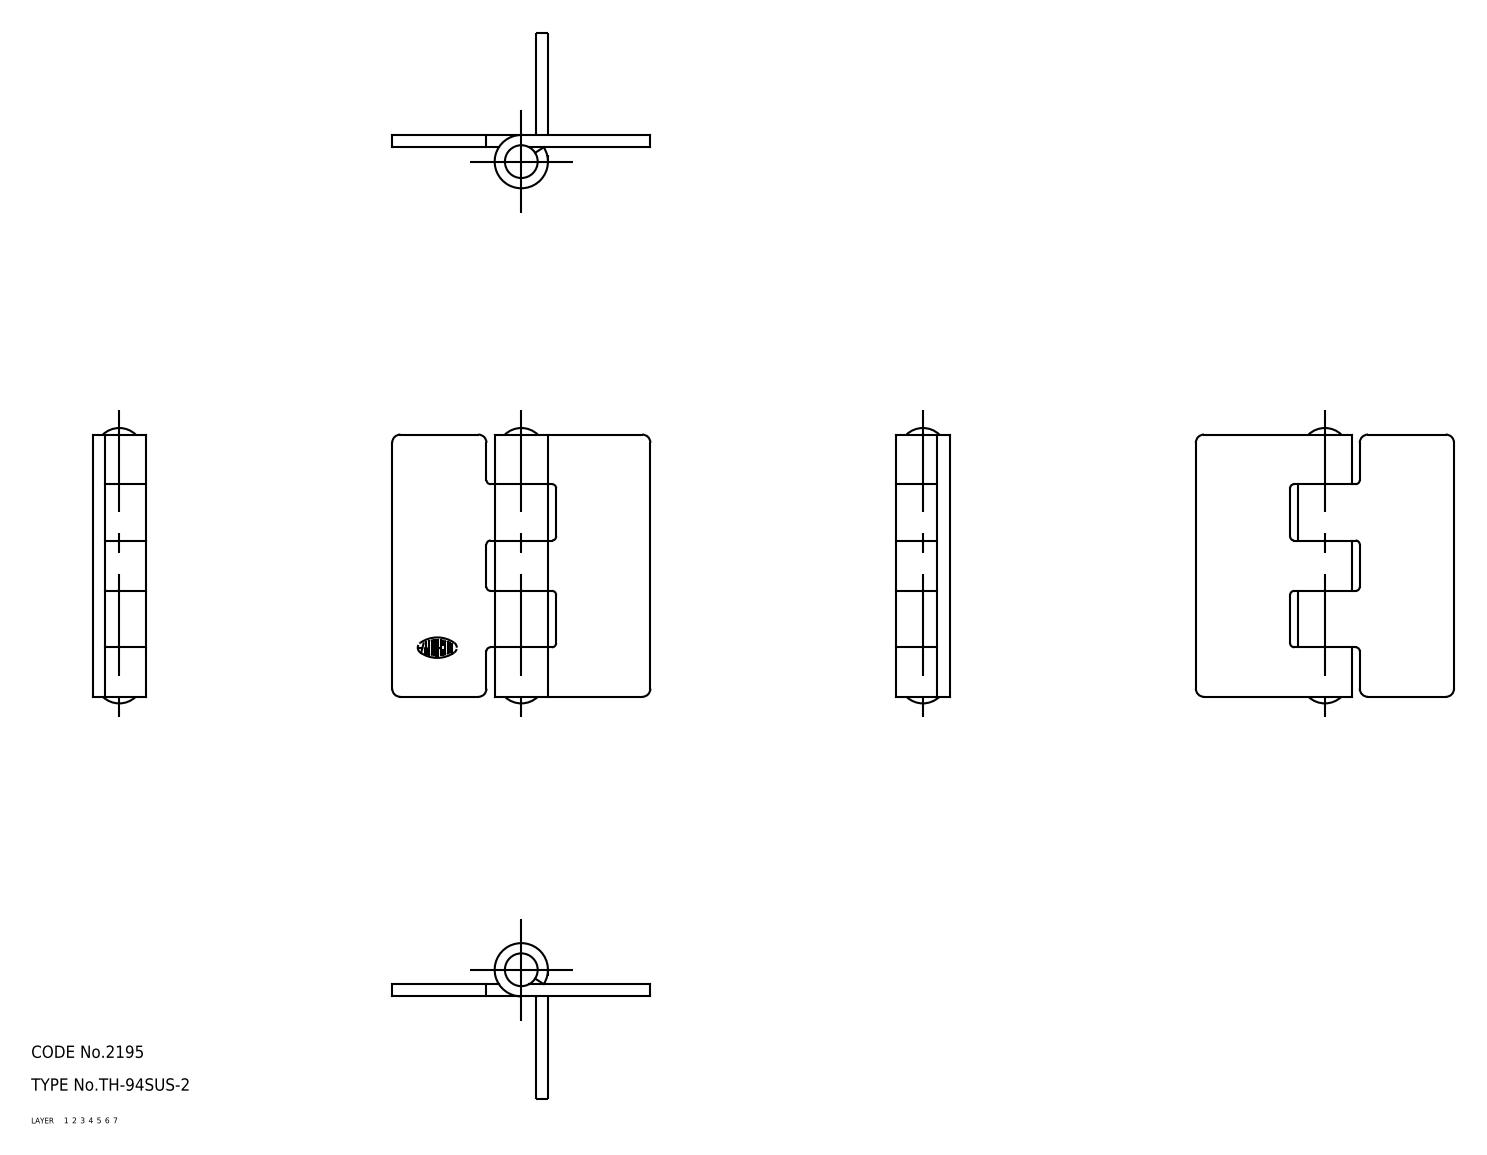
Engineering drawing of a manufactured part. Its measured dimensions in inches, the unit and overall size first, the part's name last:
Units: inches
Overall size (bounding box): 2.646 × 2.48 × 0.512
Volume: 1.103 in³ · Surface area: 21.63 in²
Bodies: 3 solids, 58 faces (0 planar, 0 cylindrical, 58 other)
Part name (STEP PRODUCT): hinge piece_B; hinge piece_A; shaft; TH_94SUS_2_19283_36
STEP written by: CADfix (AUTOMOTIVE_DESIGN)
